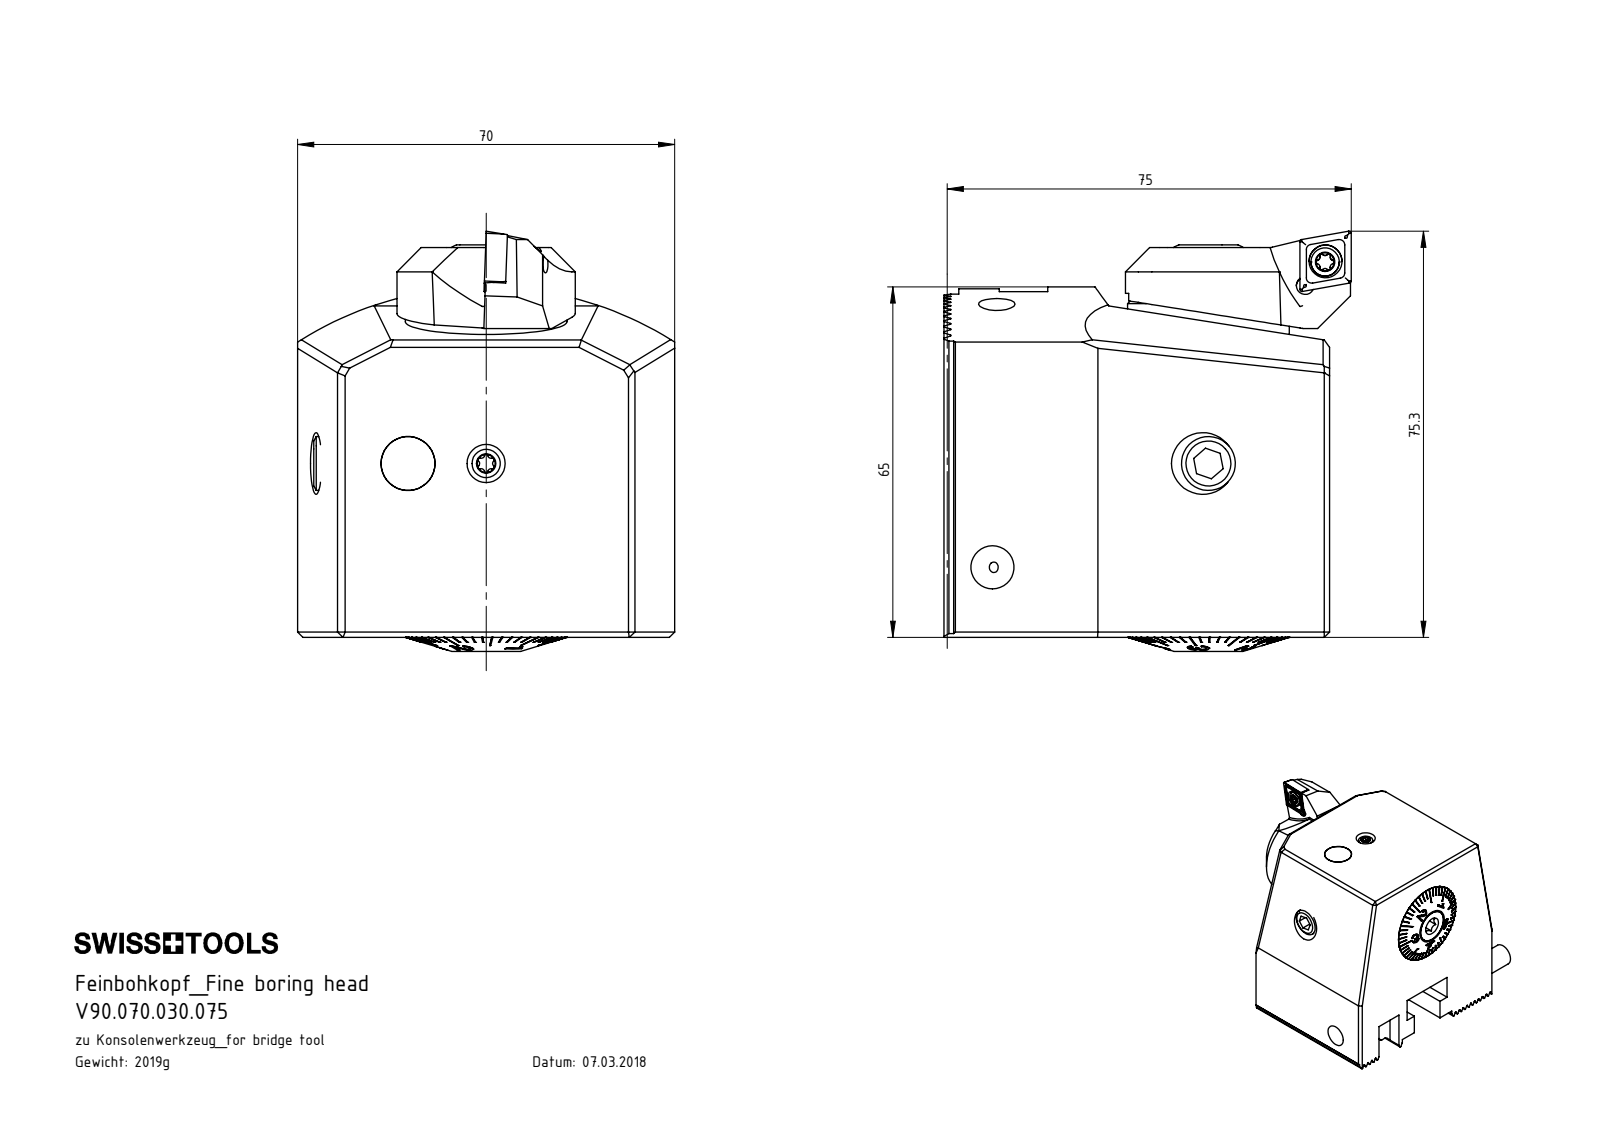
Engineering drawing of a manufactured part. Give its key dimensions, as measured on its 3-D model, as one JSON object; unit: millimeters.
{"part_name": "VK1-F0U.001.075_C; F72-BG2.015.020_B; WCB-ER2.001.009_A; ISO 4028 - M8 x 35 (+8 more)", "step_written_by": "SolidWorks 2017 (AUTOMOTIVE_DESIGN)", "units": "millimeters", "bodies": {"solids": 15, "faces": 631, "planar": 375, "cylindrical": 89, "other": 167}, "overall_size": [82, 75.4, 71.58], "volume_mm3": 249990, "surface_area_mm2": 56315, "round_holes": [[8, 3], [3.3, 2], [8.5, 2], [4.2, 1], [5, 1], [6.8, 1], [10, 1], [11.75, 1], [12, 1], [12.4, 1], [13, 1], [14, 1]], "round_bosses_or_shafts": [[10, 2], [30, 1], [29.98, 1], [29.9, 1], [25, 1], [18, 1], [16, 1], [11.95, 1]], "partial_cylinders_radius": [[0.14, 22], [0.34, 6], [0.59, 6], [3.2, 3], [0.5, 2], [1, 1], [3.5, 1], [5.25, 1]], "face_to_face_distances": [1.73, 5.2, 8.66, 6.93, 3.46, 70, 52.33, 43.3, 24.5, 45.5], "hole_center_spacings": [7, 14.5, 44.08, 44.46, 47.91]}
